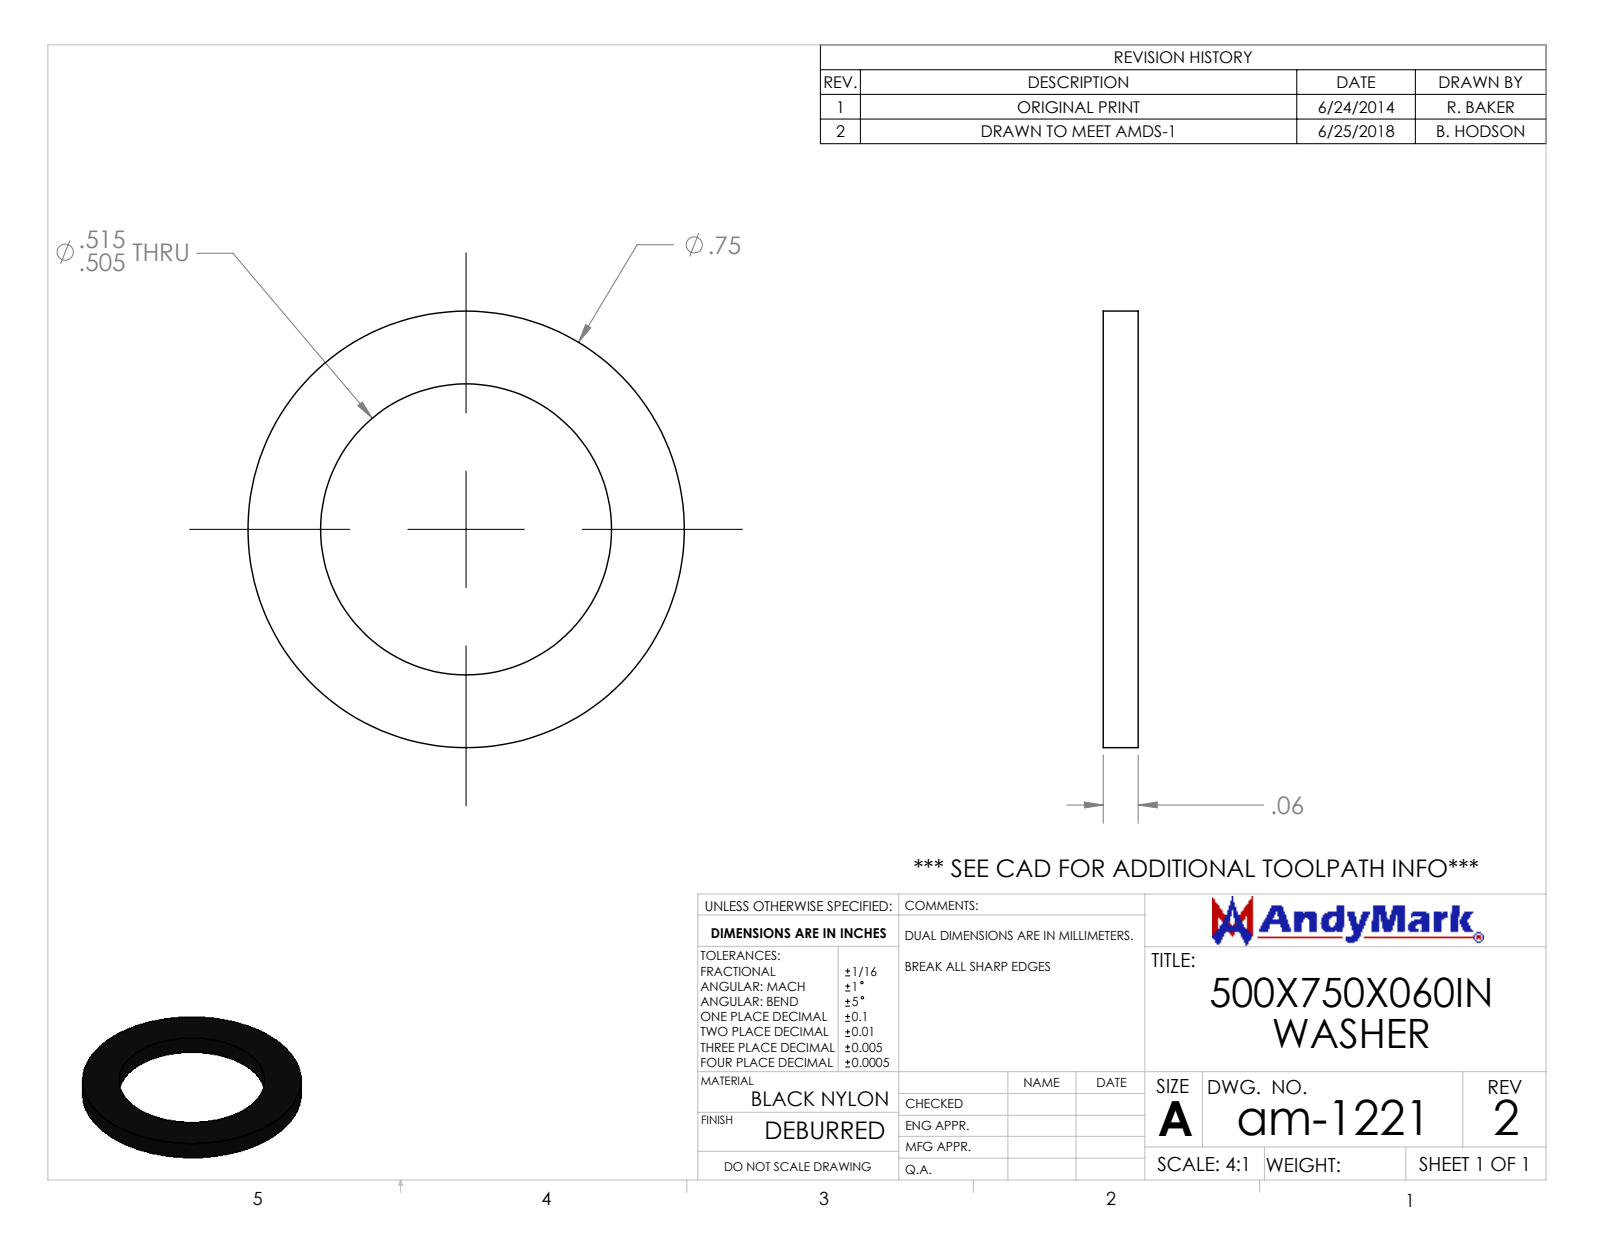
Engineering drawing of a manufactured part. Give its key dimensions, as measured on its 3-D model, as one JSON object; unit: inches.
{"part_name": "am-1221 0.5'''''''' i.d. Plastic Washer REV2", "step_written_by": "SolidWorks 2017 (AUTOMOTIVE_DESIGN)", "units": "inches", "bodies": {"solids": 1, "faces": 6, "planar": 2, "cylindrical": 4, "other": 0}, "overall_size": [0.75, 0.75, 0.06], "volume_in3": 0.015, "surface_area_in2": 0.726, "round_holes": [[0.5, 1]], "round_bosses_or_shafts": [[0.75, 1]], "face_to_face_distances": [0.06]}
